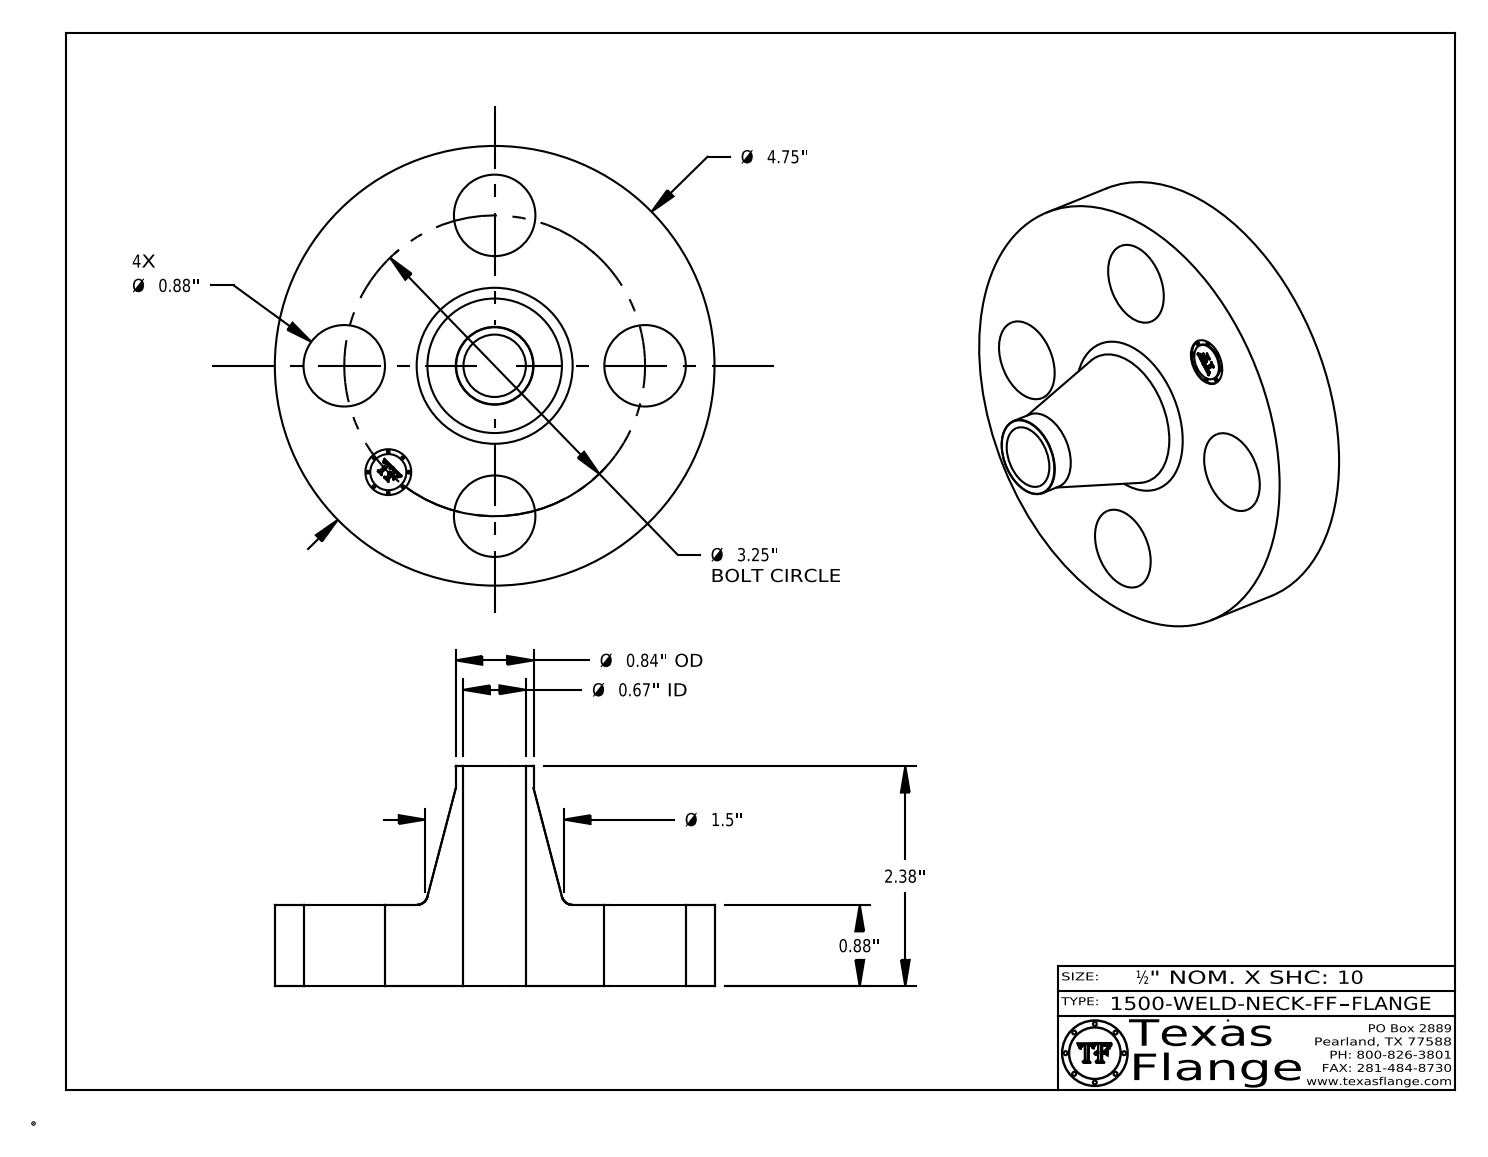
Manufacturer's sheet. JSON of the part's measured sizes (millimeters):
{"part_name": "1500-WELD-NECK-FF", "step_written_by": "CATIA V5 STEP AP214 (AUTOMOTIVE_DESIGN)", "units": "millimeters", "bodies": {"solids": 1, "faces": 408, "planar": 368, "cylindrical": 34, "other": 6}, "overall_size": [120.7, 120.7, 60.5], "volume_mm3": 231500, "surface_area_mm2": 39960, "round_holes": [[22.4, 4], [12.6, 1], [17.1, 1]], "round_bosses_or_shafts": [[0.8, 8], [120.7, 1], [21.3, 1], [9.9, 1]], "face_to_face_distances": [22.4, 60.5, 38.1, 22, 0.4, 38.5, 3.8, 3.7, 0.7, 2.4], "hole_center_spacings": [41.3, 58.4, 31.6, 76.3, 82.6]}
